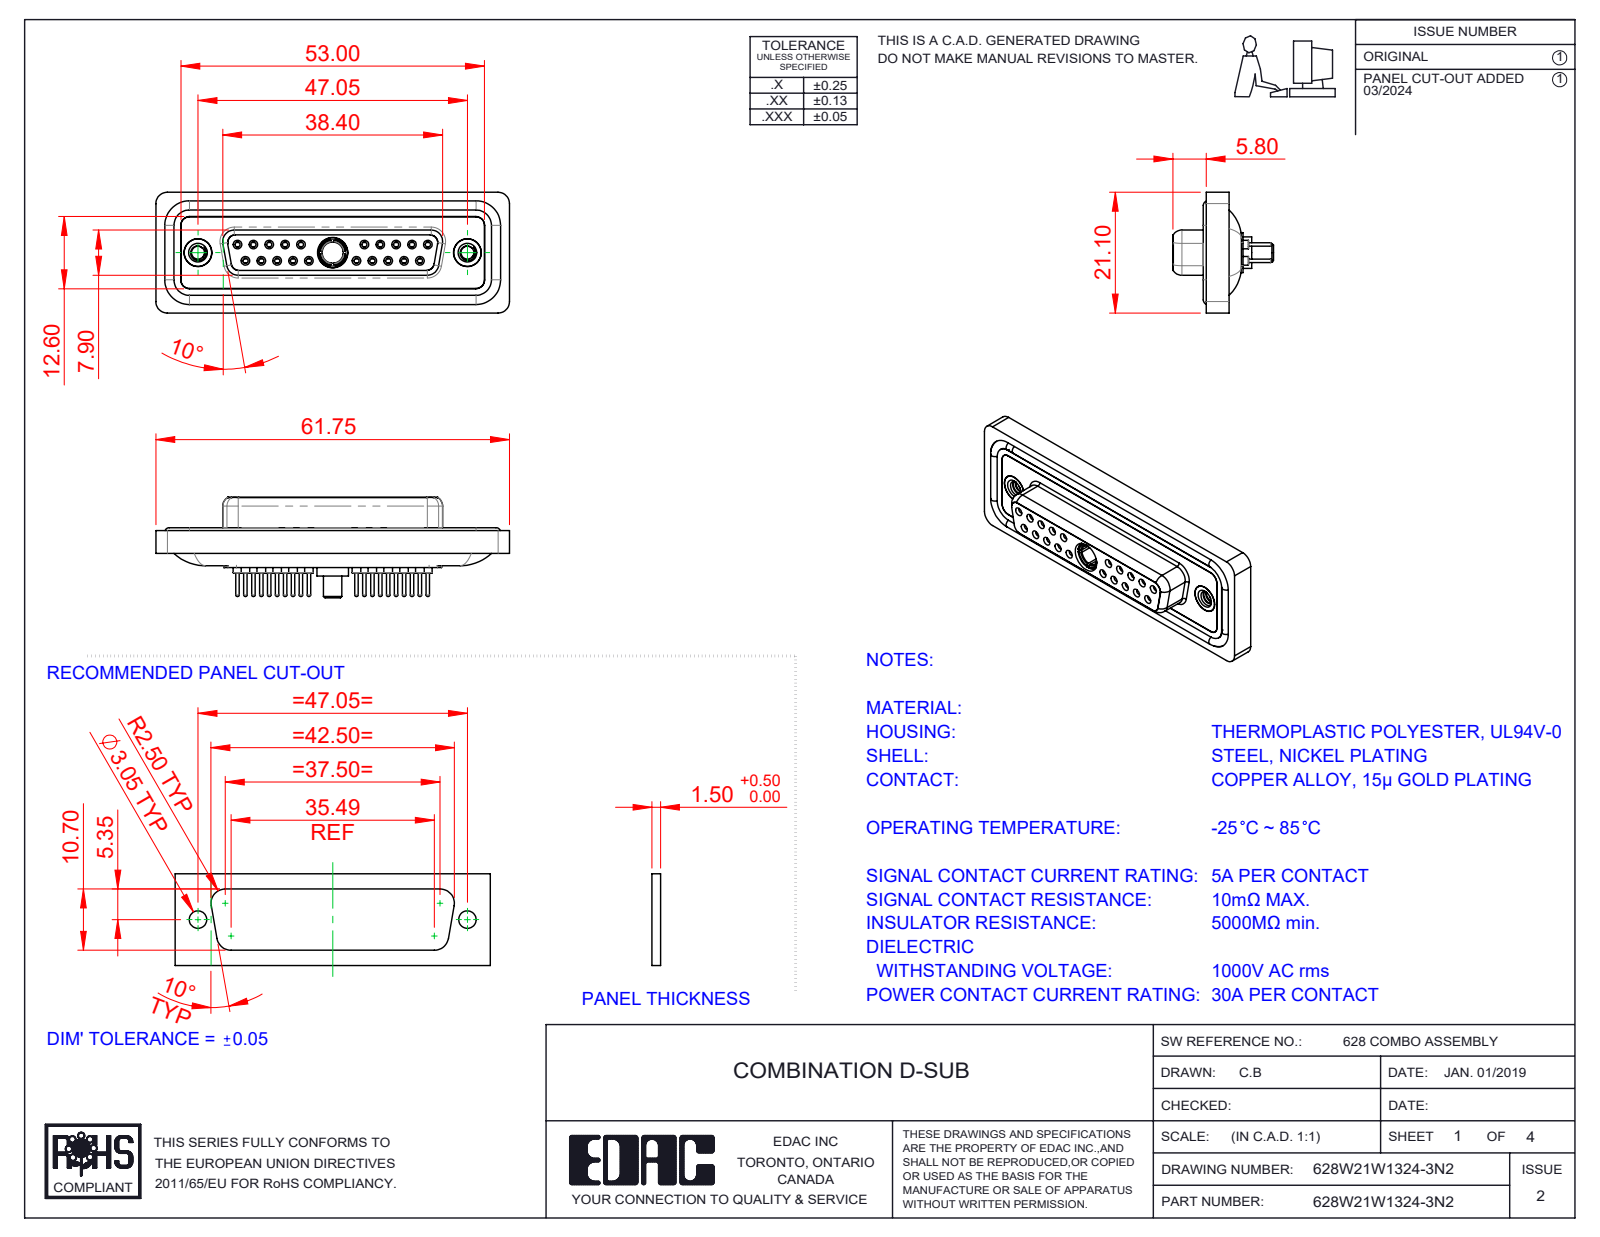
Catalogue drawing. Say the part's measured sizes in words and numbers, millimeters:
The part is named "628Combo Contact Row 2_24; 628Combo Housing_21W1; 628Combo Waterproof Housing_25 Contacts; 628Combo Contact Row 1_24 (+5 more)". Its 3-D file was written by "SolidWorks 2023 (CONFIG_CONTROL_DESIGN)". It is 29 solids with 1560 faces: 434 planar, 591 cylindrical and 535 other. Overall it measures 61.75 by 21.1 by 17.55 millimeters. Its volume is 8 381 cubic millimeters and its surface area 14 006 square millimeters. Round holes: 20 of diameter 0.9, 20 of diameter 1.1, 20 of diameter 1.5, 20 of diameter 2, 10 of diameter 1.6, 10 of diameter 1.7, 3 of diameter 4.85, 2 of diameter 2.26, 2 of diameter 4, 2 of diameter 4.05, 2 of diameter 5, 1 of diameter 3.7. Round bosses or shafts: 20 of diameter 2.2, 20 of diameter 0.6, 14 of diameter 1.6, 2 of diameter 4.95, 2 of diameter 4.8, 1 of diameter 5.5, 1 of diameter 5.2, 1 of diameter 4.96. Partial cylindrical surfaces (rounded edges, fillets, slot ends): 22 of radius 1.5, 18 of radius 2, 8 of radius 1.35, 8 of radius 1.6, 4 of radius 0.25, 4 of radius 0.5, 4 of radius 0.6, 4 of radius 0.65. The main face-to-face distances are 0.4, 1.8, 7.45, 6.6, 5.65, 0.5, 1.6, 7.05, 2.9, 1.1. The hole center spacings are 3.16, 2.77, 5.54, 5.03, 8.31, 7.48, 16.62, 19.39.
